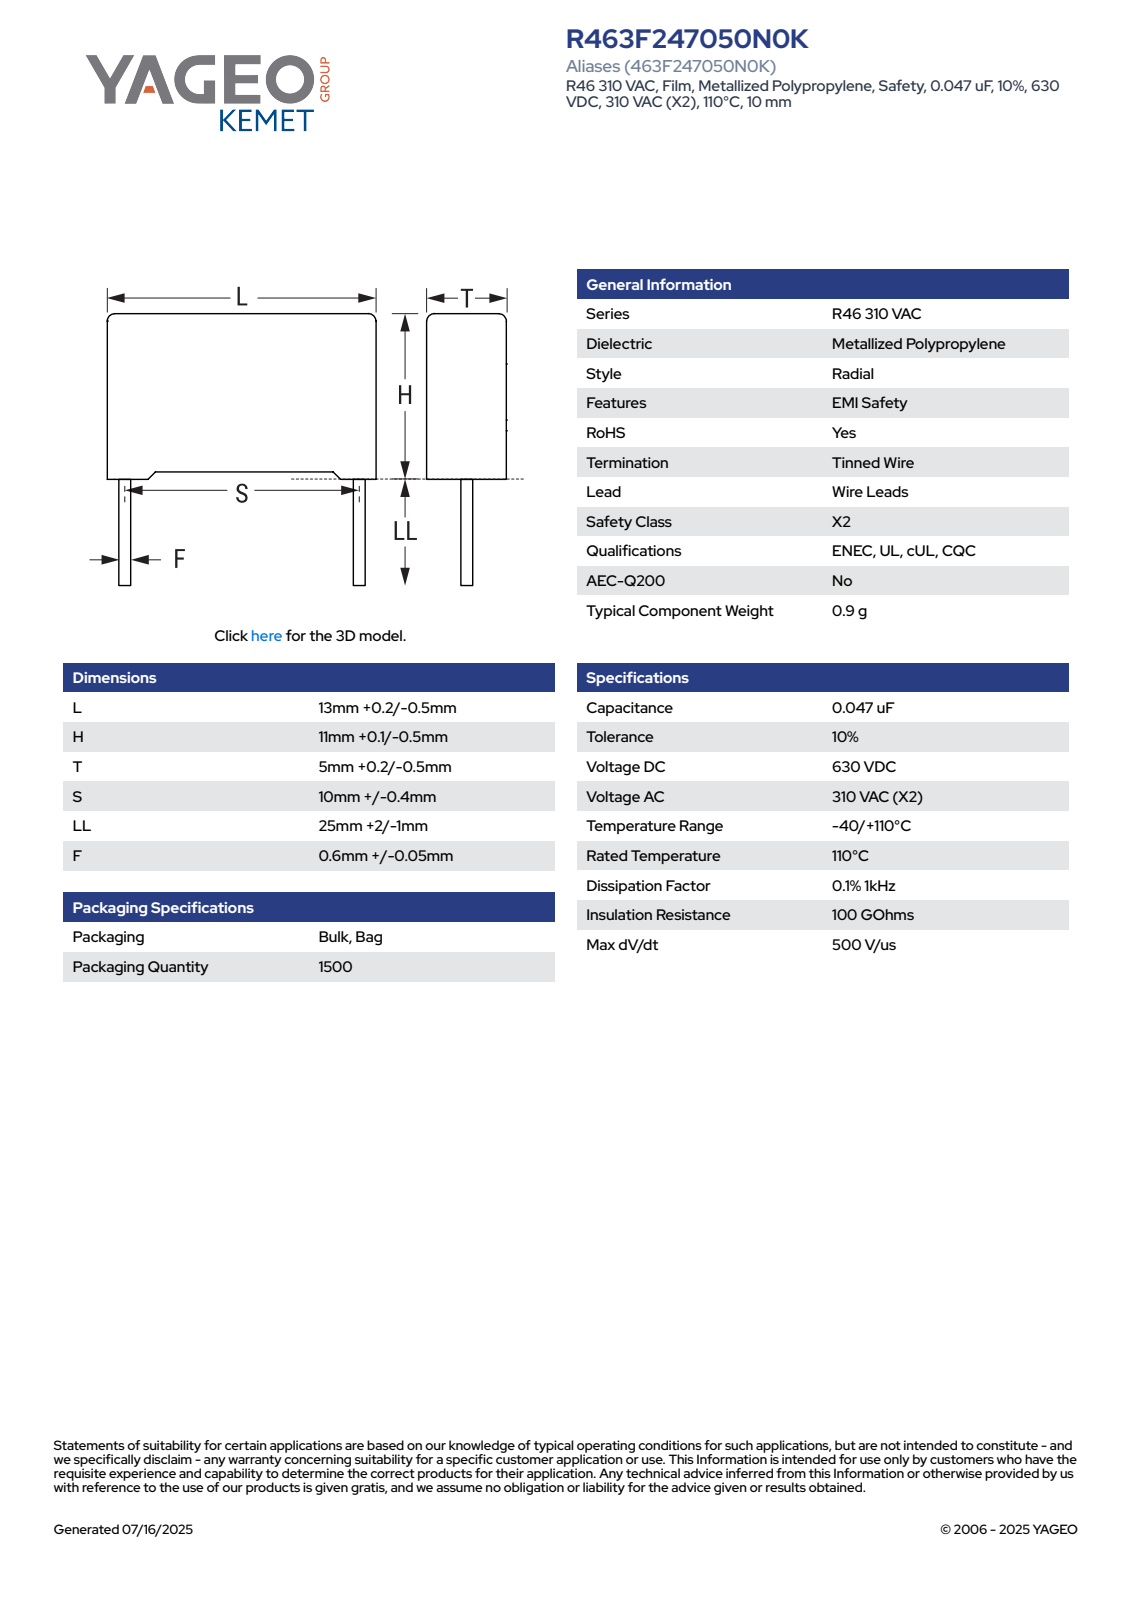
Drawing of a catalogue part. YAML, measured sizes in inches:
part_name: "CFR_RB2_13X11X5_L13.2H11.1T5.2S10LL27F0.65"
step_written_by: "SolidWorks 2021 (AUTOMOTIVE_DESIGN)"
units: inches
bodies: {solids: 4, faces: 85, planar: 77, cylindrical: 8, other: 0}
overall_size: [1.5, 0.52, 0.205]
volume: 0.045
surface_area: 1.05
round_bosses_or_shafts:
  - {diameter: 0.026, count: 2}
partial_cylinders:
  - {radius: 0.02, count: 4}
face_to_face_distances: [0.205, 0.52, 0.407, 0.017, 0.187, 0.03, 0.437, 0.17, 0.502, 0.015]
